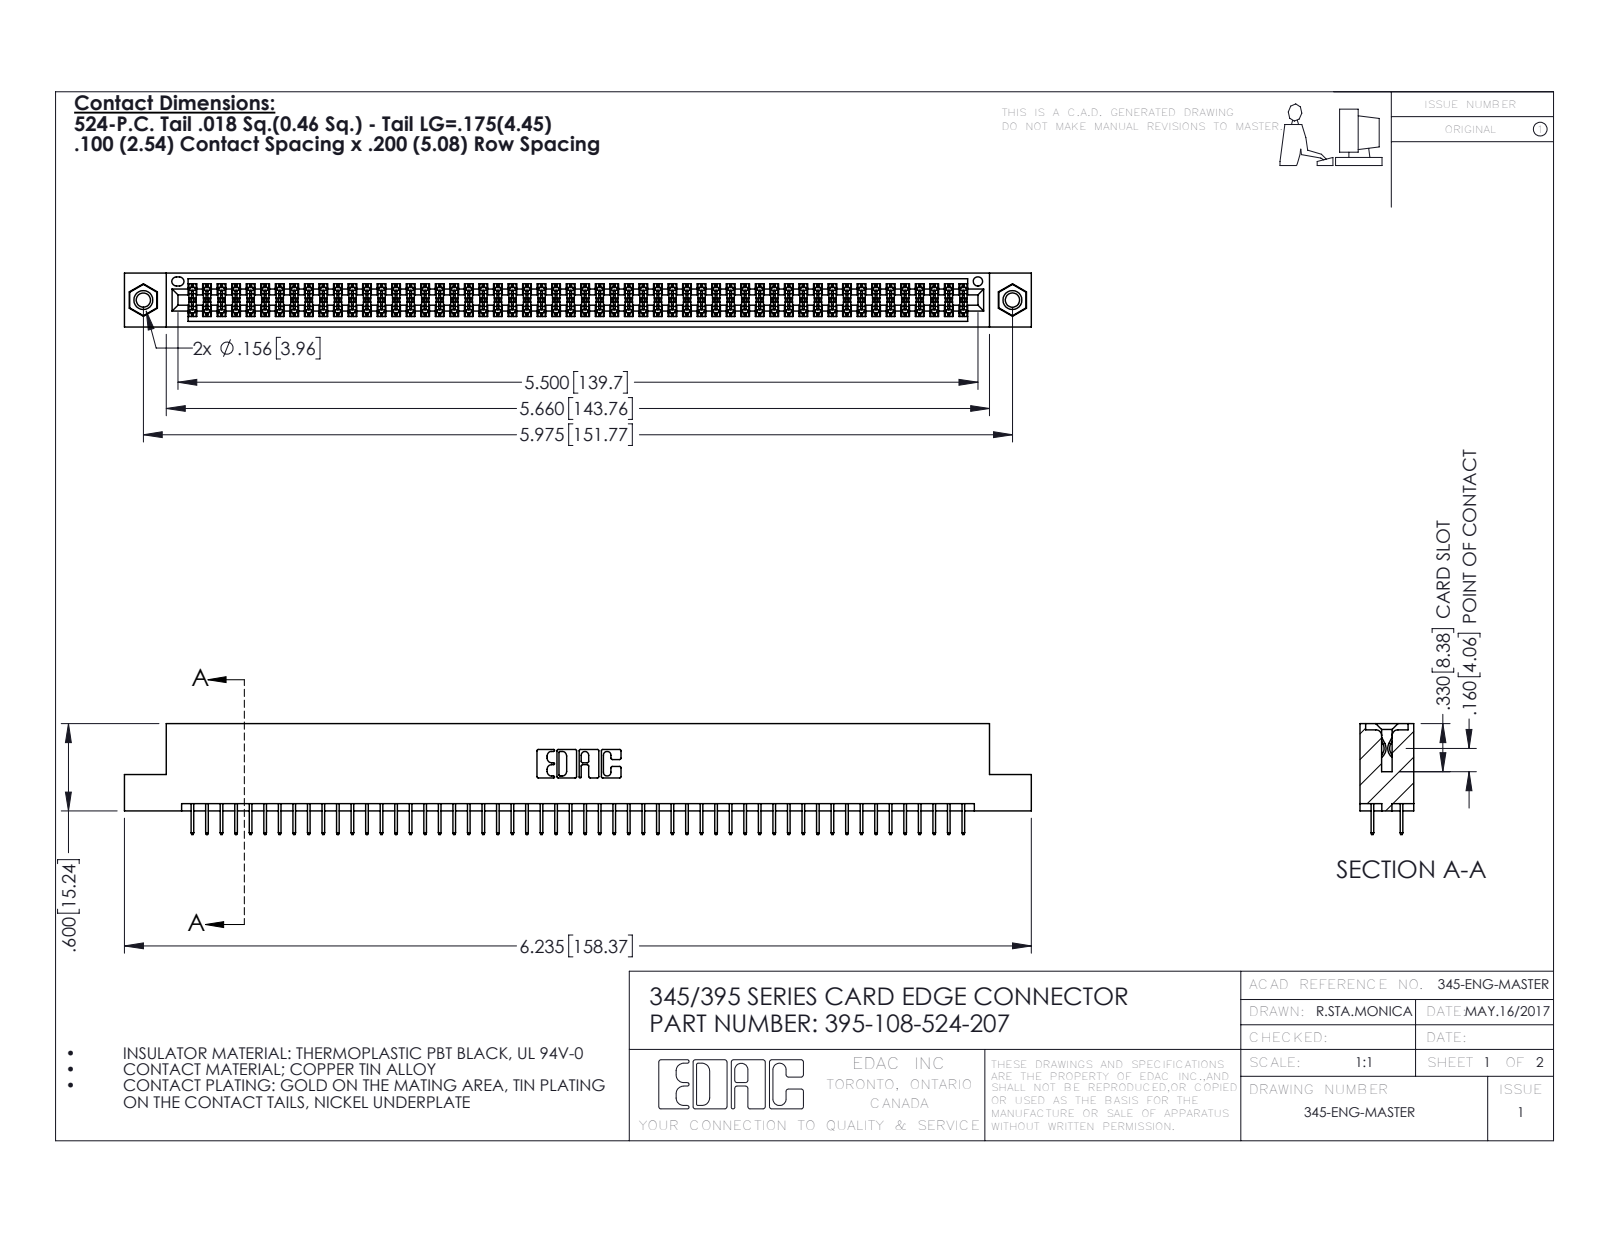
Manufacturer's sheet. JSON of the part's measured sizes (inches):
{"part_name": "345 Part_Flush Mounting Lugs - 0.156 Dia-TI; 395-108-524-207; 345-292-001_345-293-124; 345-250-001_345-250-005-103", "step_written_by": "SolidWorks 2016 (CONFIG_CONTROL_DESIGN)", "units": "inches", "bodies": {"solids": 111, "faces": 6018, "planar": 4324, "cylindrical": 1678, "other": 16}, "overall_size": [6.235, 0.762, 0.37], "volume_in3": 0.935, "surface_area_in2": 34.83, "round_holes": [[0.098, 2], [0.125, 2], [0.156, 2], [0.064, 1]], "round_bosses_or_shafts": [[0.155, 2]], "partial_cylinders_radius": [[0.006, 162], [0.01, 22], [0.007, 6], [0.031, 6], [0.026, 3], [0.014, 2], [0.019, 2], [0.022, 2]], "face_to_face_distances": [0.072, 0.298, 0.2, 0.37, 0.098, 0.272, 0.025, 0.225, 0.072, 0.175], "hole_center_spacings": [0.27, 5.739, 5.975]}
